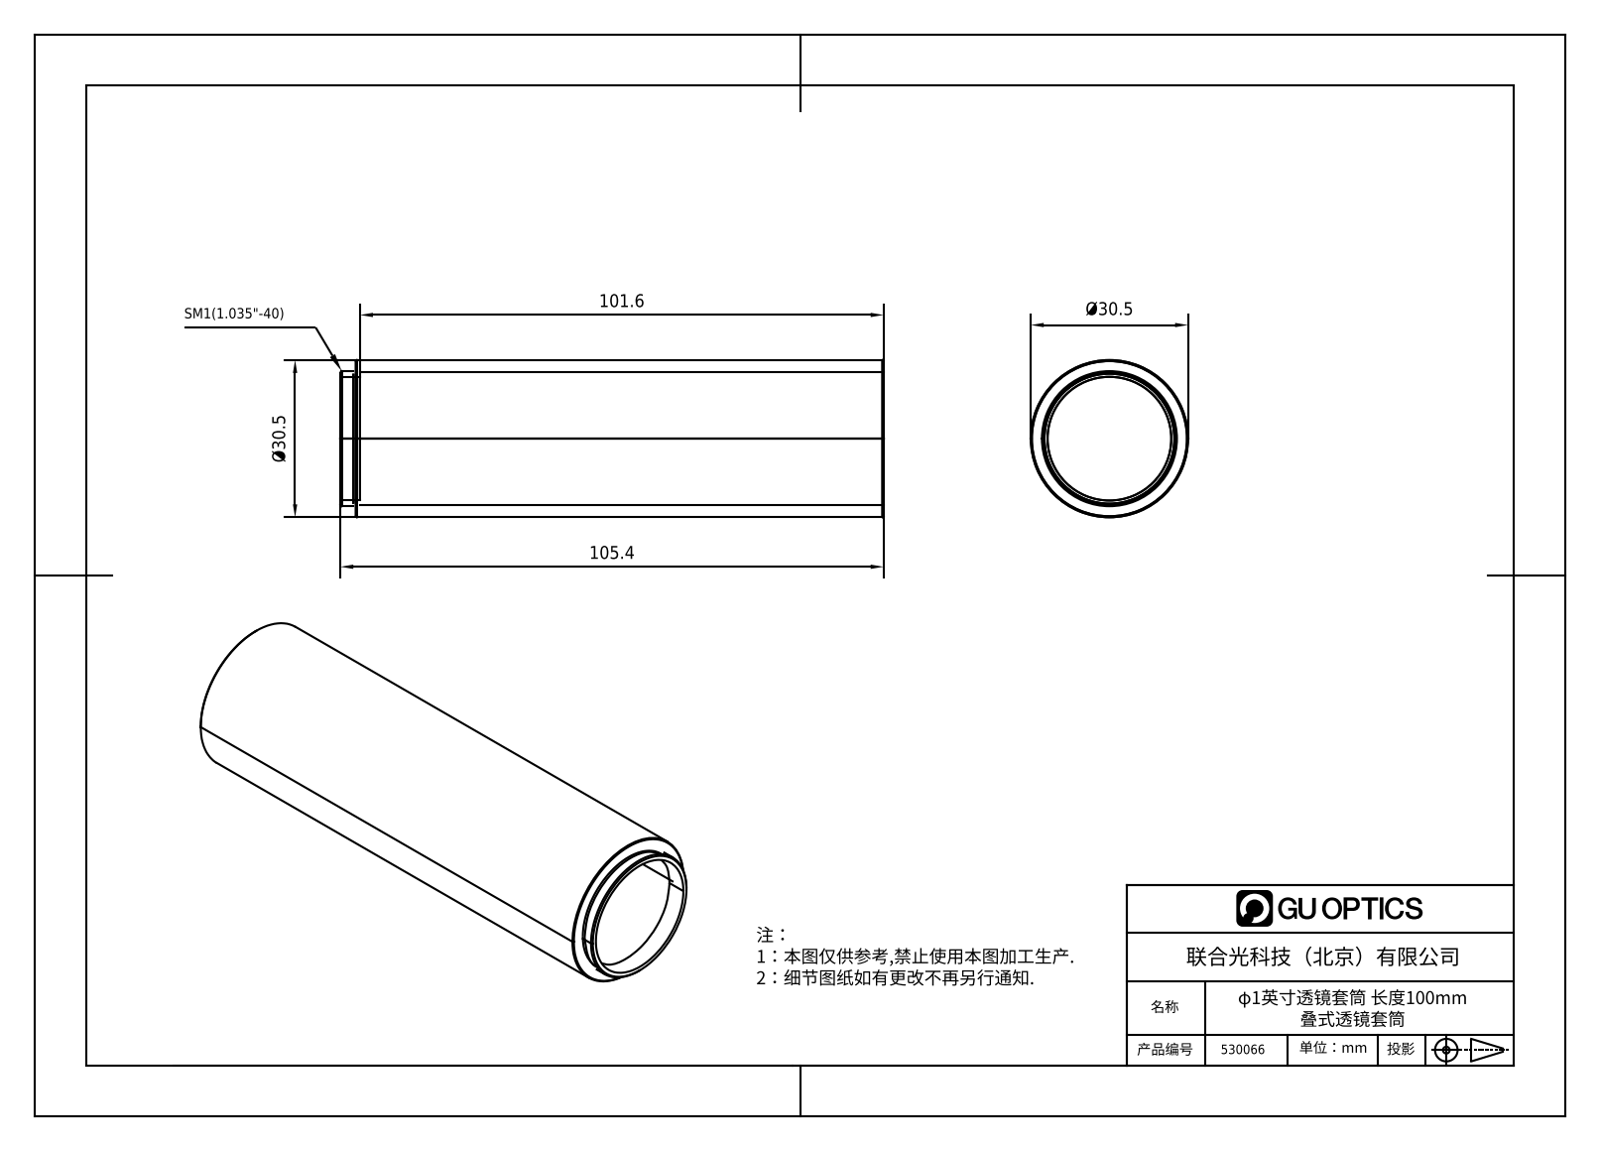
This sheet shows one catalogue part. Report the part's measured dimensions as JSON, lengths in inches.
{"part_name": "1.7.1.15_ZTC-1-4.0_SM1标准型4.0英寸层叠式透镜套筒", "step_written_by": "SolidWorks 2018 (AUTOMOTIVE_DESIGN)", "units": "inches", "bodies": {"solids": 0, "faces": 34, "planar": 11, "cylindrical": 12, "other": 11}, "overall_size": [4.15, 1.201, 1.201], "round_holes": [[0.906, 1], [0.945, 1], [1.01, 1]], "round_bosses_or_shafts": [[1.201, 1], [1.031, 1], [0.992, 1]], "face_to_face_distances": [4.031, 4.15, 0.118, 0.028, 4.004, 4.122, 0.039]}
